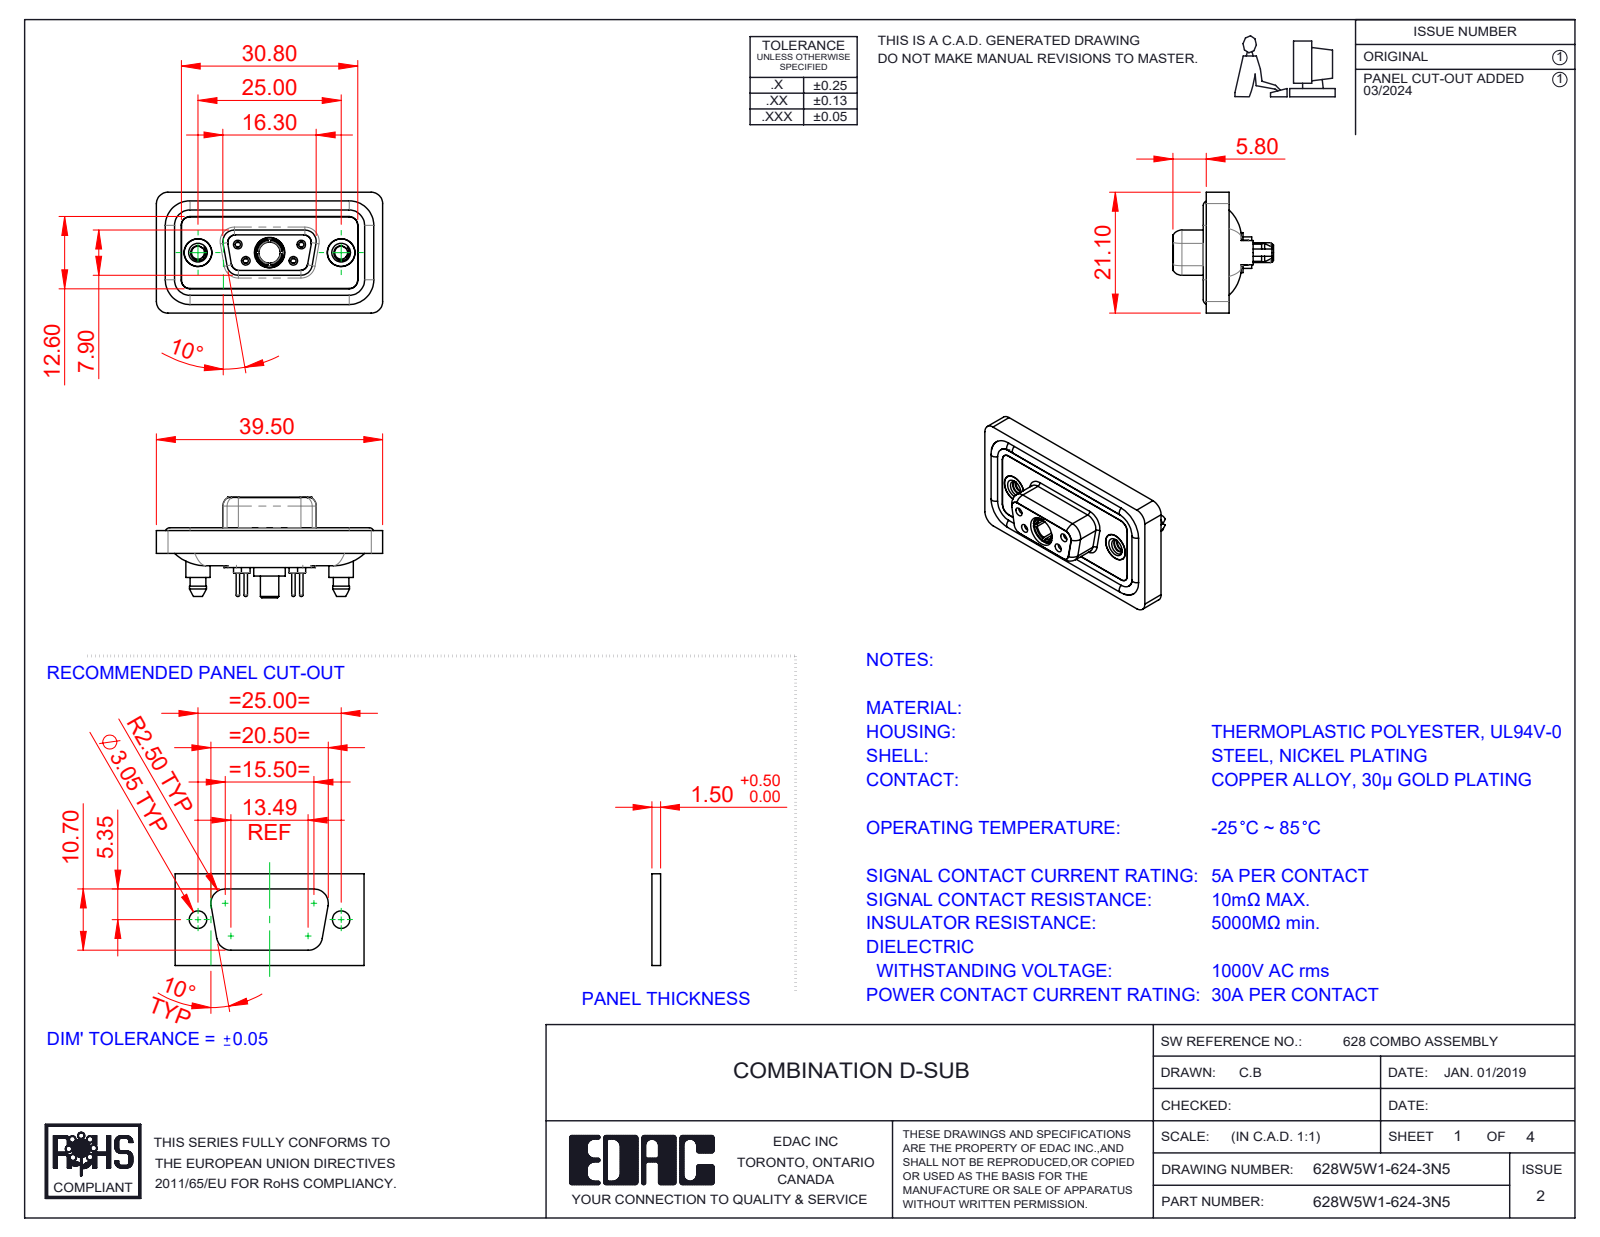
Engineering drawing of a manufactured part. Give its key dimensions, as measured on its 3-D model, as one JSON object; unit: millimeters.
{"part_name": "628Combo Waterproof Housing_09 Contacts; 628Combo Shell Front_09 Contacts; 628Combo Shell Rear_09 Contacts; Power Socket_30A S (+5 more)", "step_written_by": "SolidWorks 2023 (CONFIG_CONTROL_DESIGN)", "units": "millimeters", "bodies": {"solids": 13, "faces": 730, "planar": 210, "cylindrical": 319, "other": 201}, "overall_size": [39.5, 21.1, 17.55], "volume_mm3": 4908, "surface_area_mm2": 7973, "round_holes": [[0.9, 4], [1.1, 4], [1.5, 4], [2, 4], [4.85, 3], [1.6, 2], [1.7, 2], [2.26, 2], [4, 2], [4.05, 2], [5, 2], [3.7, 1]], "round_bosses_or_shafts": [[1.6, 6], [2.2, 4], [0.6, 4], [5.4, 2], [4.95, 2], [4.8, 2], [4.25, 2], [5.5, 1]], "partial_cylinders_radius": [[1.5, 24], [2, 18], [1.6, 10], [1.35, 8], [0.25, 4], [0.5, 4], [0.6, 4], [0.65, 4]], "face_to_face_distances": [0.4, 2.9, 1.1, 1.8, 1.6, 0.5, 5.65, 7.45, 5.35, 3.6], "hole_center_spacings": [3.16, 5.72, 7.1, 12.5, 18.1, 4.39, 4.4, 8.31]}
